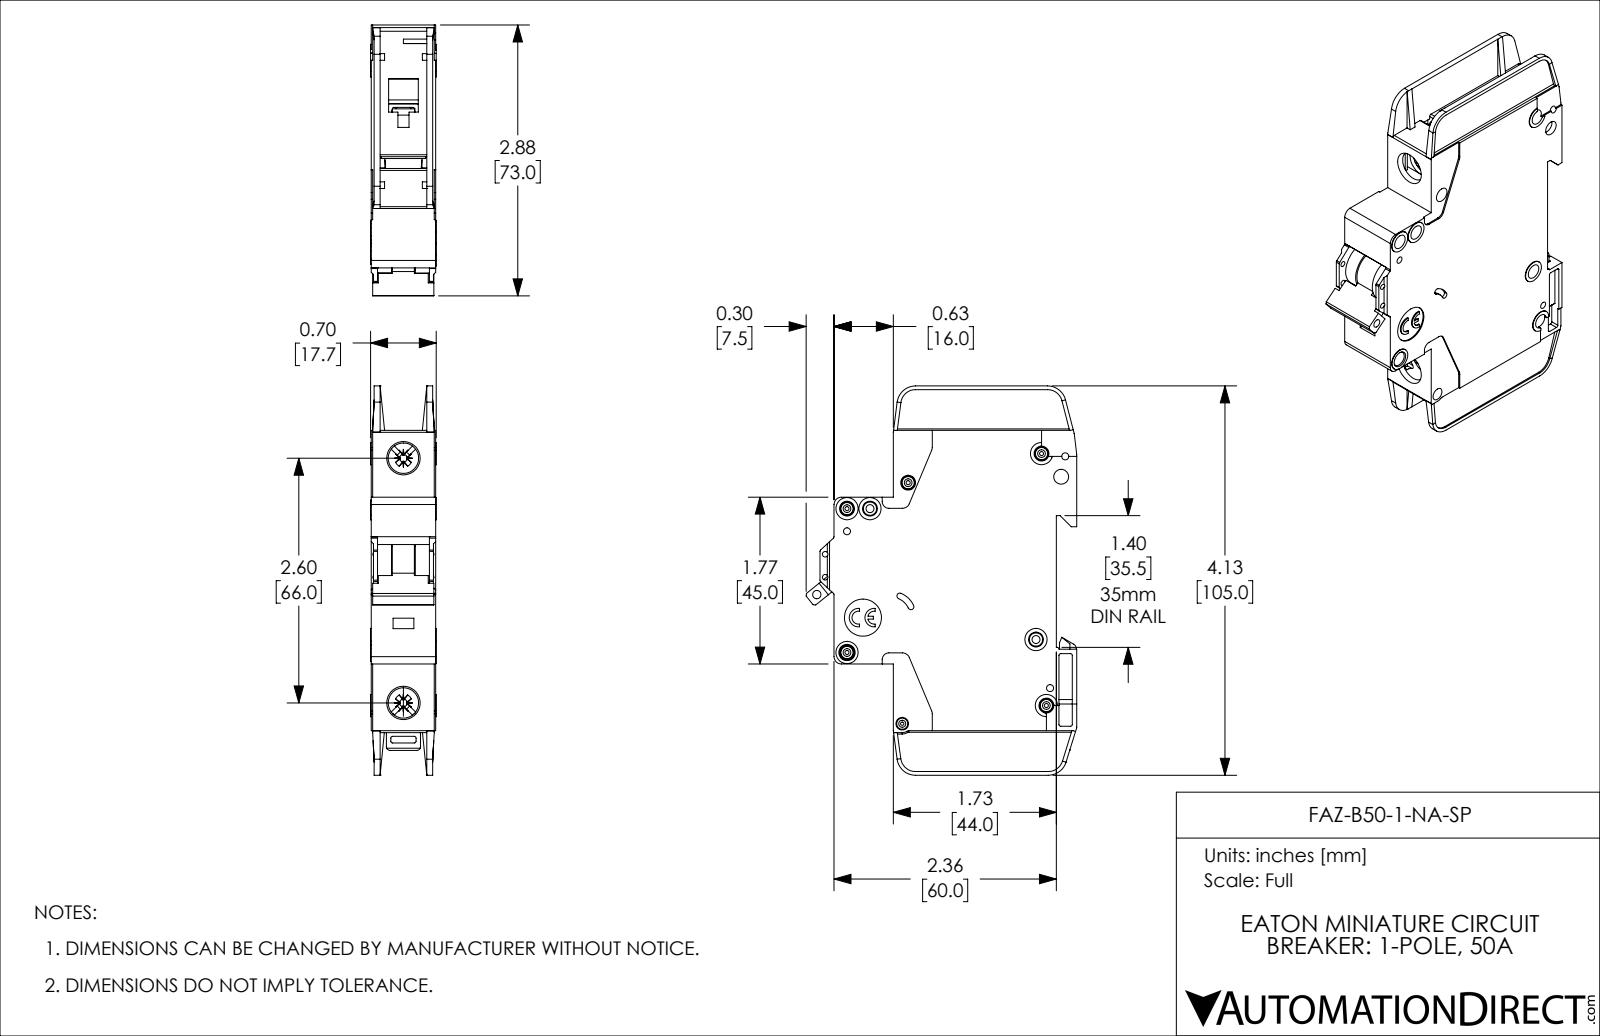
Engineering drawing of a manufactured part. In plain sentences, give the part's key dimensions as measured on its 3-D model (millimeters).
The part is named "FAZ-B50-1-NA-SP". Its 3-D file was written by "SolidWorks 2019 (AUTOMOTIVE_DESIGN)". It is 1 solid with 1127 faces: 671 planar, 357 cylindrical and 99 other. Overall it measures 105 by 73.1 by 17.7 millimeters. Its volume is 76 720 cubic millimeters and its surface area 26 460 square millimeters. Round holes: 8 of diameter 4, 5 of diameter 1.1, 4 of diameter 1.9, 2 of diameter 1.5, 2 of diameter 2.2, 2 of diameter 8.2, 1 of diameter 0.9, 1 of diameter 2.3, 1 of diameter 2.5, 1 of diameter 3.4, 1 of diameter 10. Round bosses or shafts: 5 of diameter 3.3, 4 of diameter 6, 2 of diameter 3, 1 of diameter 2.5. Partial cylindrical surfaces (rounded edges, fillets, slot ends): 42 of radius 0.5, 10 of radius 0.4, 10 of radius 1, 8 of radius 2, 5 of radius 5, 4 of radius 0.2, 4 of radius 0.7, 4 of radius 1.1. The main face-to-face distances are 1.2, 17.4, 15, 16.2, 2.4, 13.8, 0.4, 0.8, 12.6, 14.6. The hole center spacings are 6.2, 13.6, 22.1, 4.8, 5.1, 5.2, 5.6, 6.1.
